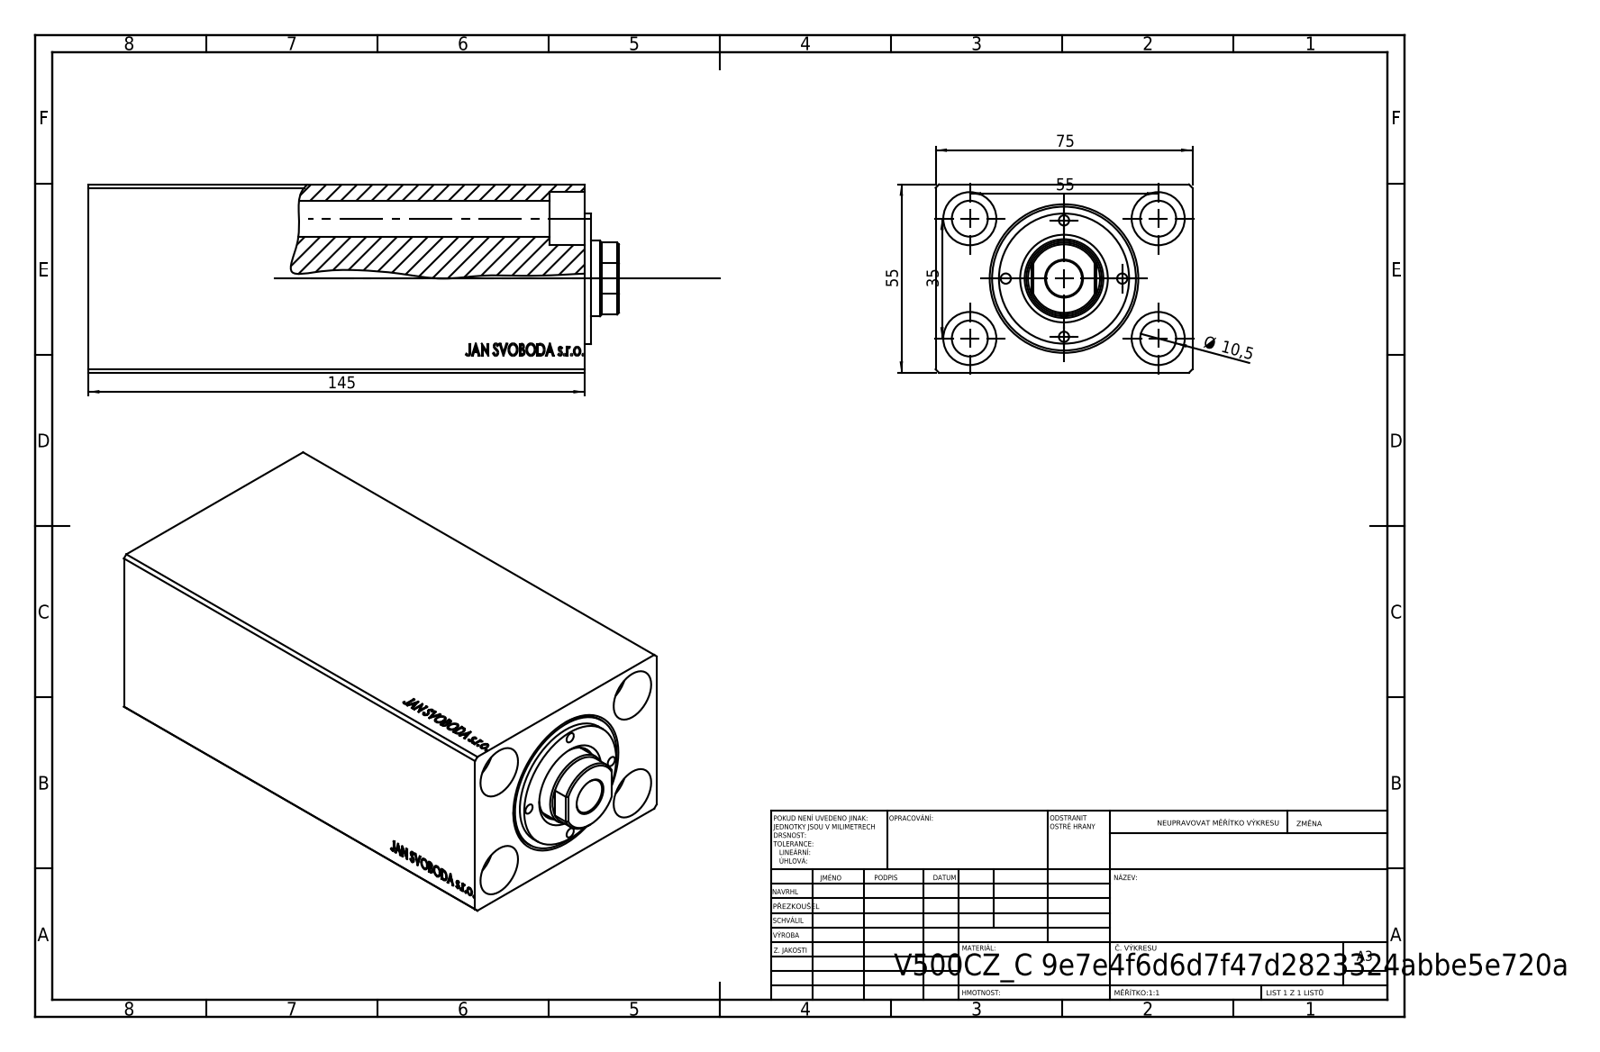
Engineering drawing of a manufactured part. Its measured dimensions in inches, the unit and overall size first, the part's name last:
Units: inches
Overall size (bounding box): 5.709 × 2.953 × 2.165
Round holes (diameter × count): ⌀0.413 ×4, ⌀0.61 ×4, ⌀0.217 ×2, ⌀0.535 ×2, ⌀0.787 ×2, ⌀1.26 ×1, ⌀1.417 ×1, ⌀1.654 ×1
Main face-to-face distances: 2.165, 2.953, 5.709, 5.701, 0.407, 5.302, 5.177, 0.524, 0.531, 2.618
Hole centre spacings: 1.283, 1.378, 2.165, 2.567, 4.252
Volume: 23.87 in³ · Surface area: 127.1 in²
Bodies: 1 solid, 818 faces (394 planar, 42 cylindrical, 382 other)
STEP written by: SolidWorks 2019 (CONFIG_CONTROL_DESIGN)
